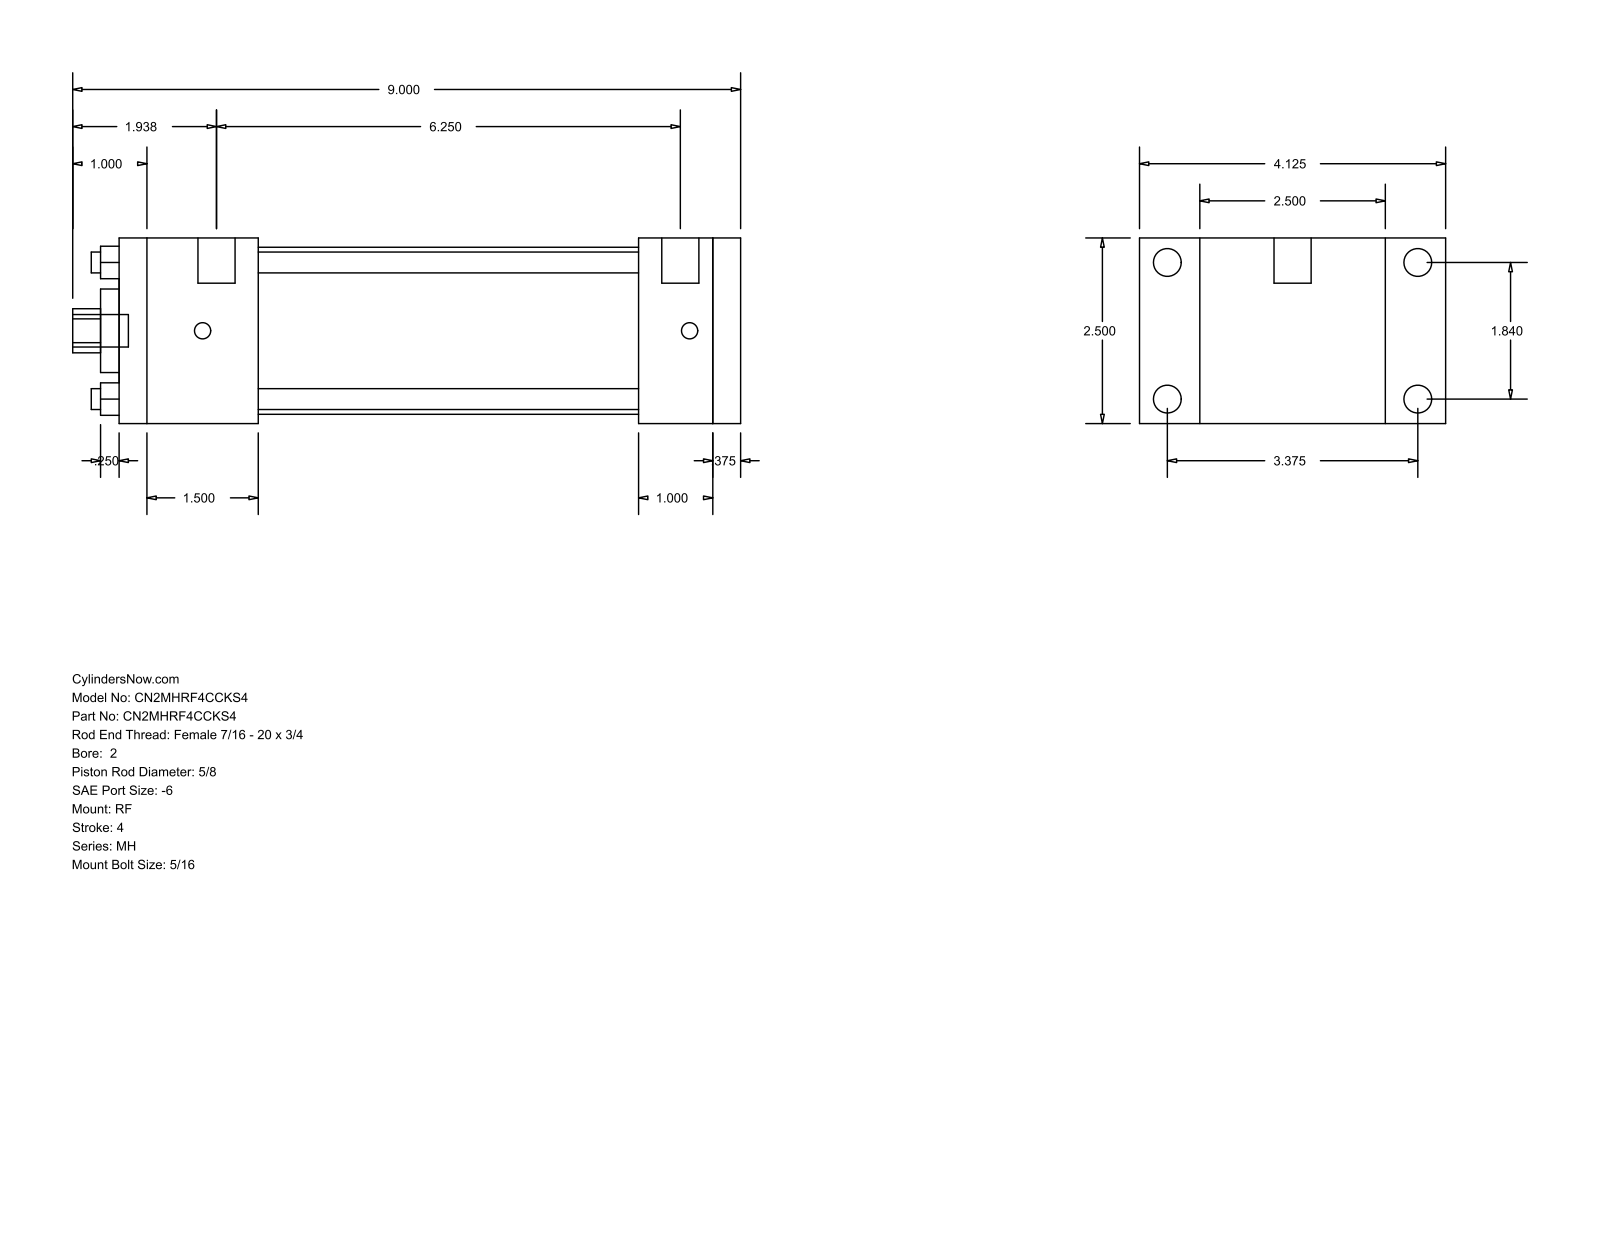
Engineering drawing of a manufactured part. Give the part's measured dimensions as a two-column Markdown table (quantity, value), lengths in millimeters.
| quantity | value |
| --- | --- |
| part name | MH_RF__0200_0.625 |
| STEP written by | GSSL Pune (CONFIG_CONTROL_DESIGN) |
| units | millimeters |
| bodies | 0 solids, 92 faces (64 planar, 28 cylindrical, 0 other) |
| overall size | 228.6 × 104.78 × 63.5 |
| round holes (diameter × count) | 7.14 × 4, 15.88 × 1, 28.57 × 1, 57.15 × 1 |
| round bosses / shafts (diameter × count) | 9.53 × 4, 5.56 × 4, 12.7 × 2, 11.11 × 1 |
| partial cylindrical surfaces (radius × count) | 7.54 × 1 |
| main face-to-face distances | 63.5, 212.72, 9.53, 203.19, 47.62, 177.8, 130.18, 155.57, 165.1, 25.39 |
| hole center spacings | 33.05, 46.74, 66.1 |
